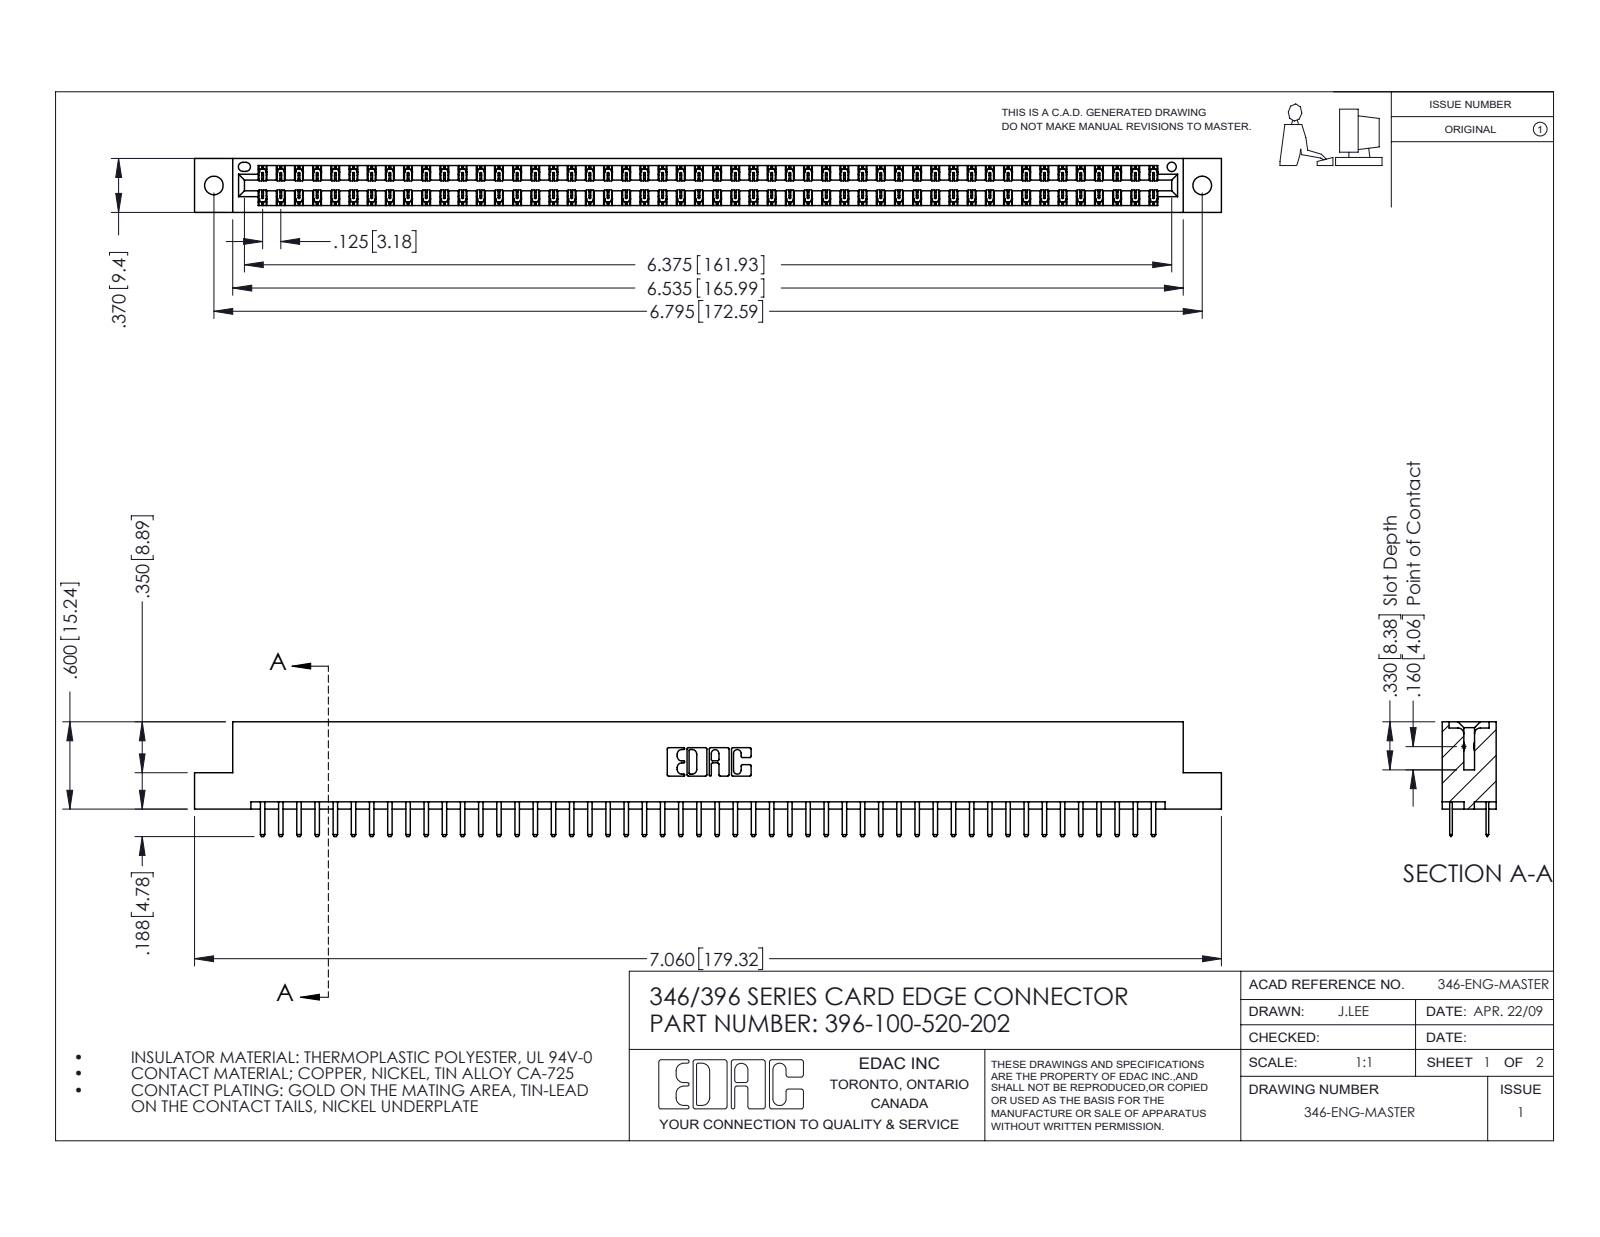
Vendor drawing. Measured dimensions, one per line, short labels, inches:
name: 346 Part_Flush Mounting Lugs - 0.128 Dia; 396-100-520-202; 345-292-001_345-293-120
written by: SolidWorks 2016 (CONFIG_CONTROL_DESIGN)
unit: in
bodies: 101 solids, 5722 faces (3776 planar, 1946 cylindrical, 0 other)
size: 7.06 × 0.788 × 0.37
volume: 1.066 in³; area: 36.83 in²
holes: 2× ⌀0.128, 1× ⌀0.064
rounds: 150× R0.006, 104× R0.01, 22× R0.01, 6× R0.007, 6× R0.031, 3× R0.026, 2× R0.014, 2× R0.022
face distances: 0.048, 0.322, 0.25, 0.37, 0.275, 0.072, 0.298, 0.025, 0.148, 0.222
hole spacings: 0.246, 6.586, 6.795
